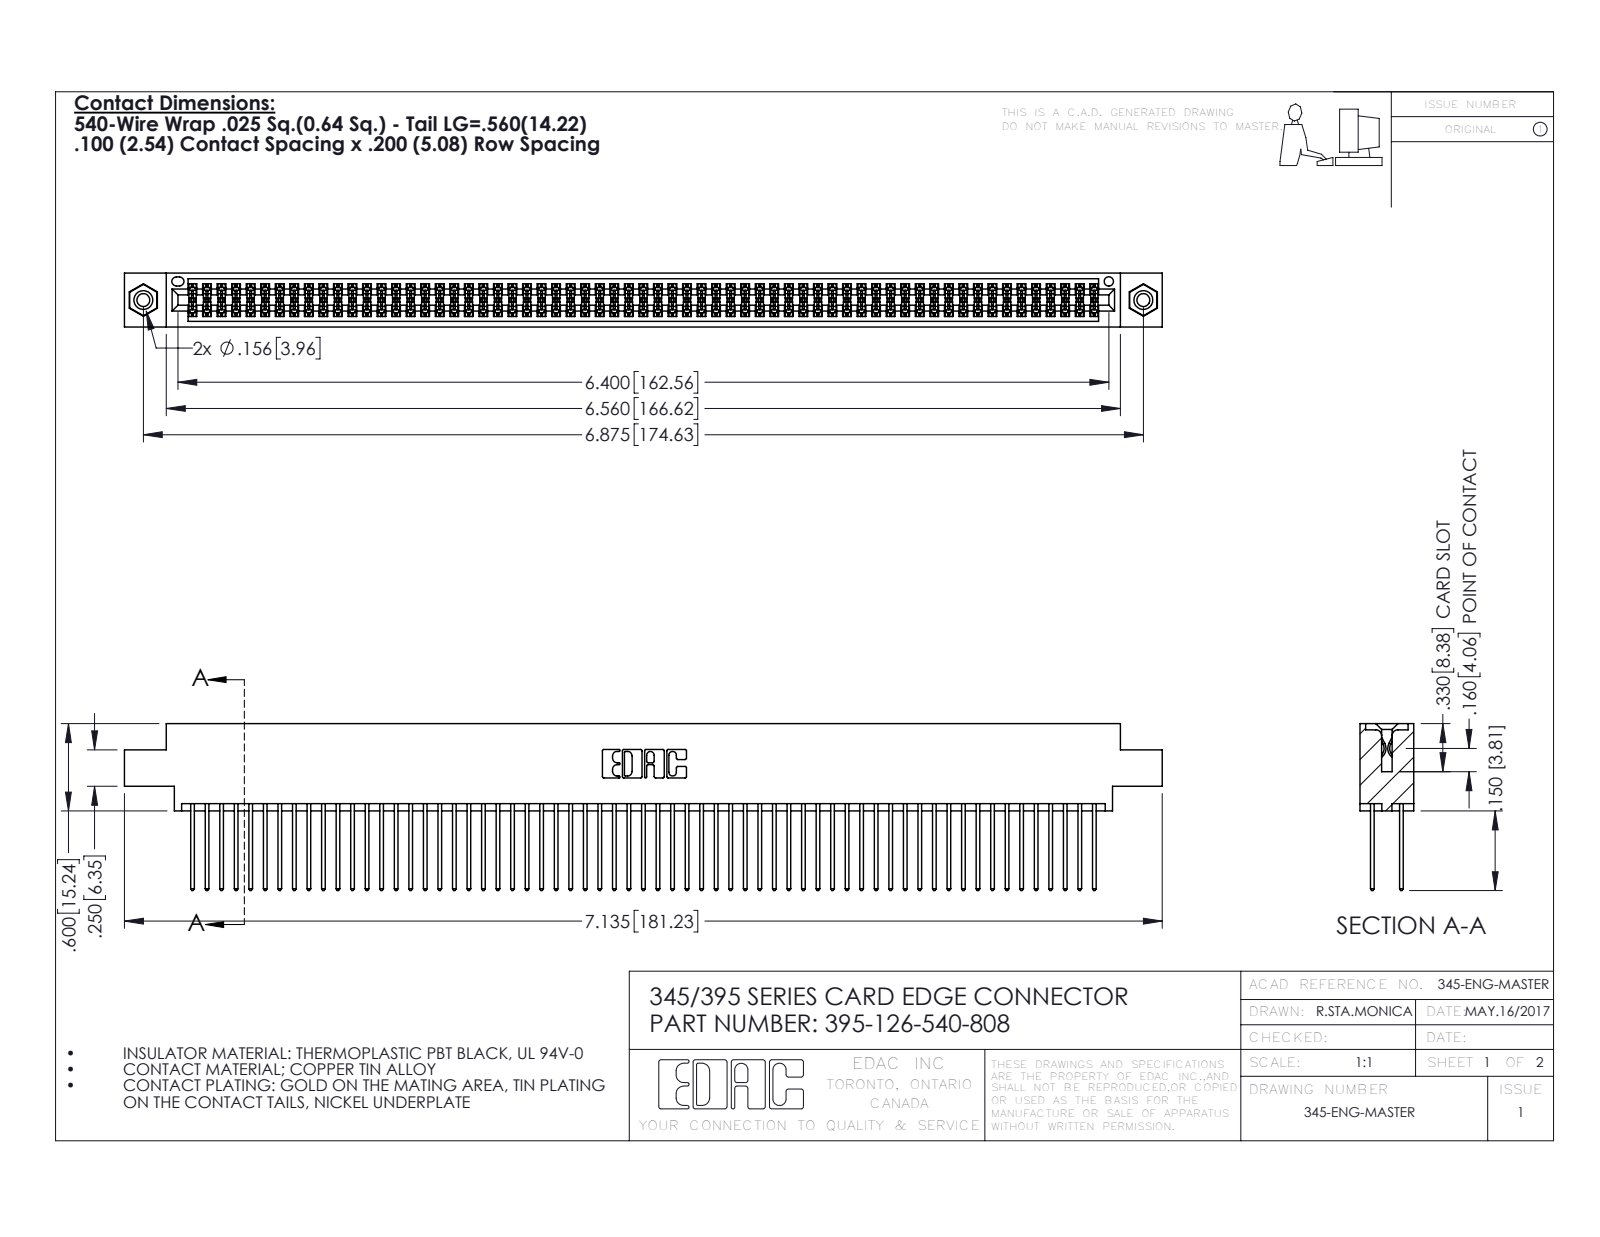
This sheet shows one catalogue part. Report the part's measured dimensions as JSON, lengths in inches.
{"part_name": "395-126-540-808; 345-250-001_345-250-003-102; 345 Part_0.170 Offset - 0.156 Dia-TI; 345-292-001_345-293-140", "step_written_by": "SolidWorks 2016 (CONFIG_CONTROL_DESIGN)", "units": "inches", "bodies": {"solids": 129, "faces": 6490, "planar": 4274, "cylindrical": 2200, "other": 16}, "overall_size": [7.135, 1.147, 0.37], "volume_in3": 1.108, "surface_area_in2": 45.91, "round_holes": [[0.089, 2], [0.125, 2], [0.156, 2], [0.064, 1]], "round_bosses_or_shafts": [[0.155, 2]], "partial_cylinders_radius": [[0.006, 189], [0.01, 126], [0.01, 22], [0.007, 6], [0.031, 6], [0.026, 3], [0.014, 2], [0.019, 2]], "face_to_face_distances": [0.072, 0.298, 0.2, 0.098, 0.272, 0.025, 0.37, 0.225, 0.175, 0.149], "hole_center_spacings": [0.27, 6.639, 6.875]}
